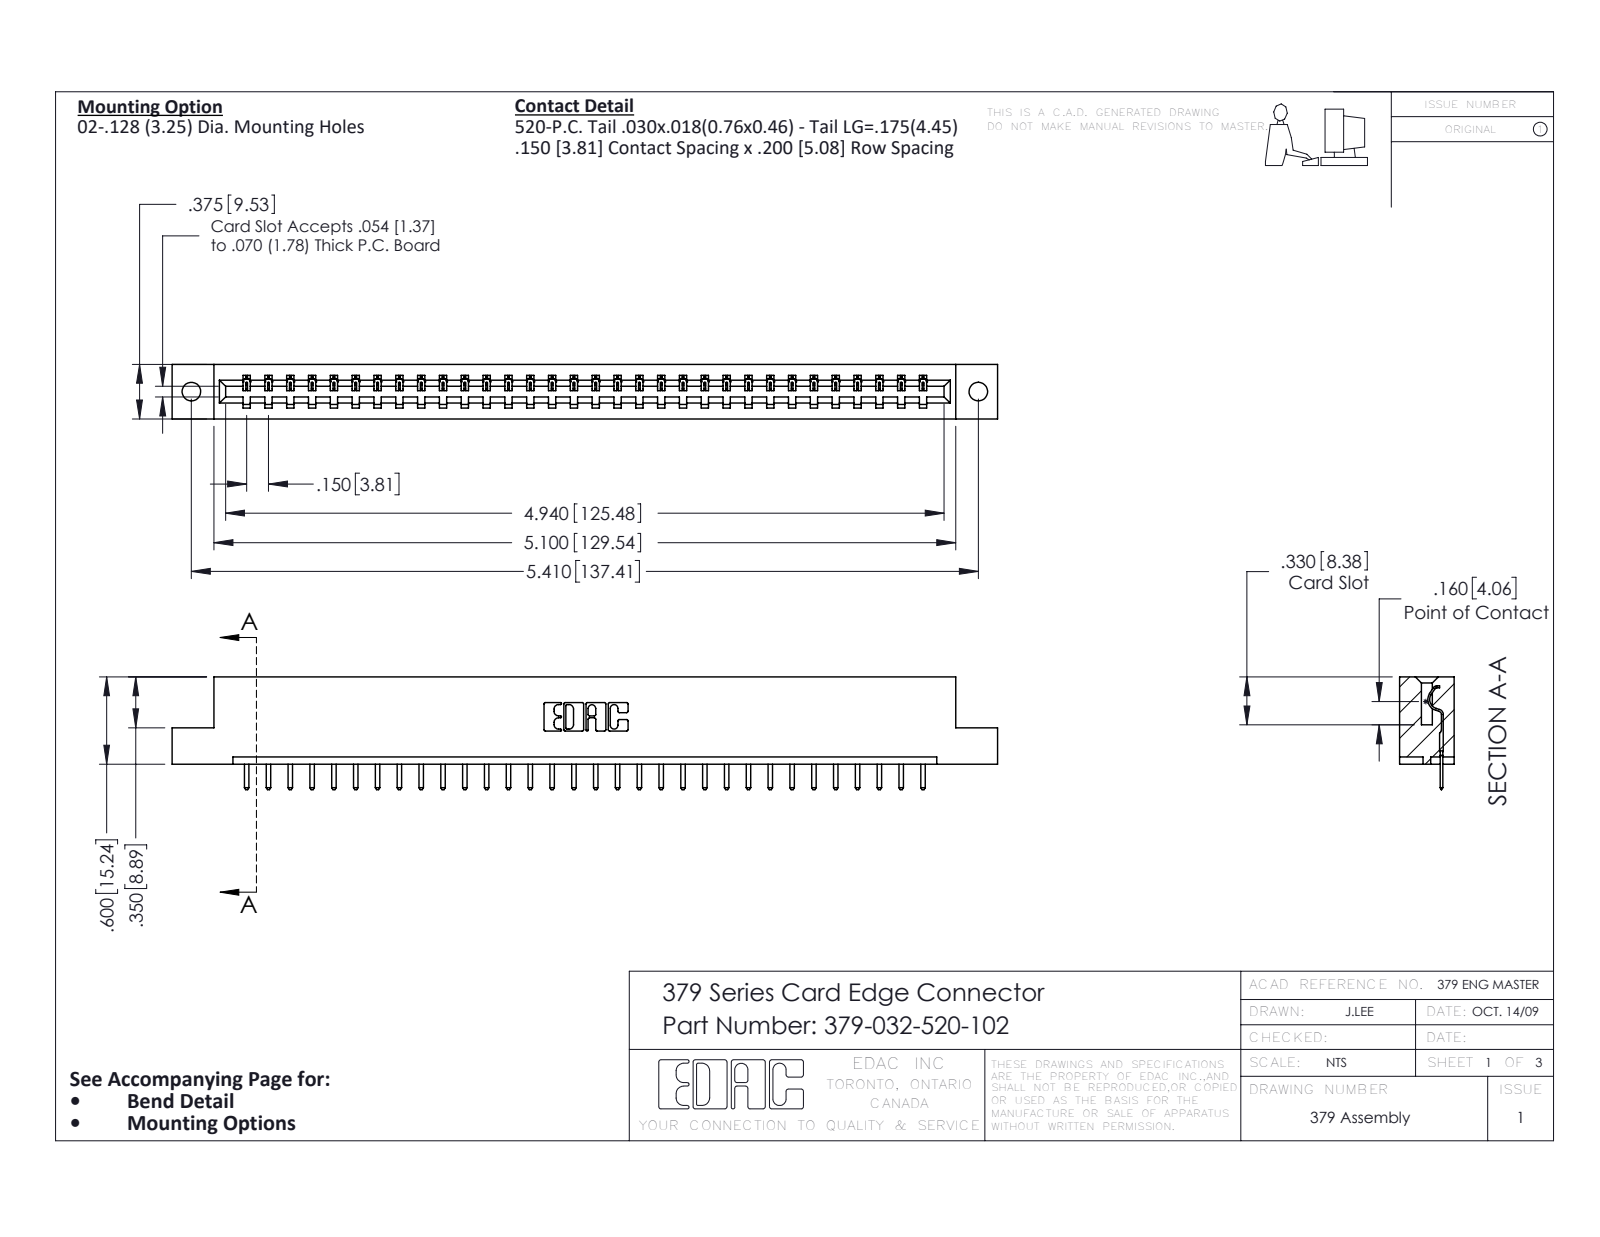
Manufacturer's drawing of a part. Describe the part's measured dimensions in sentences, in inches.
The part is named "379 Part_Flush - .128 Dia; 379-032-520-102; 345-292-001_345-293-120". Its 3-D file was written by "SolidWorks 2016 (CONFIG_CONTROL_DESIGN)". It is 33 solids with 2098 faces: 1478 planar, 620 cylindrical and 0 other. Overall it measures 5.675 by 0.775 by 0.375 inches. Its volume is 0.909 cubic inches and its surface area 22.61 square inches. Round holes: 2 of diameter 0.128. Partial cylindrical surfaces (rounded edges, fillets, slot ends): 66 of radius 0.01, 64 of radius 0.006, 22 of radius 0.01, 6 of radius 0.007, 6 of radius 0.031, 3 of radius 0.026, 1 of radius 0.014, 1 of radius 0.022. The main face-to-face distances are 0.3, 0.075, 0.375, 0.225, 0.6, 0.2, 0.55, 0.15, 0.15, 0.15. The hole center spacings are 5.41.
